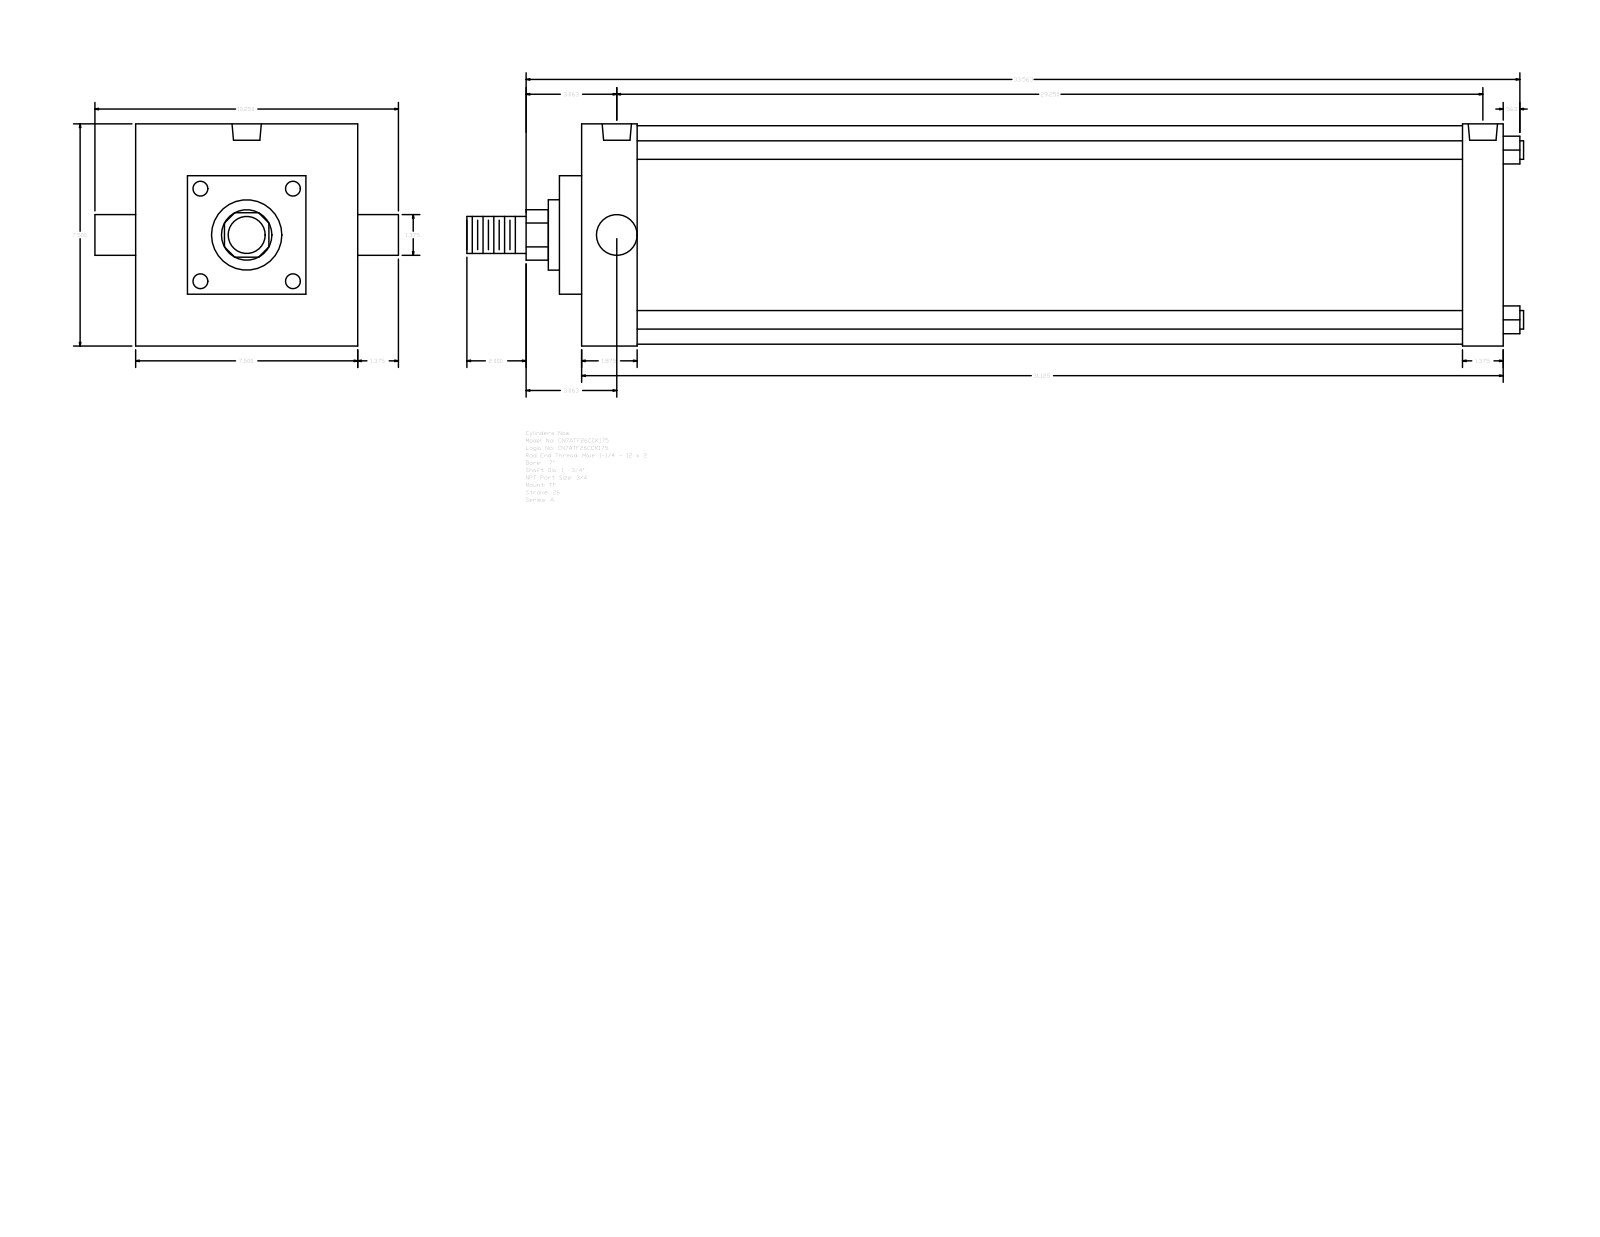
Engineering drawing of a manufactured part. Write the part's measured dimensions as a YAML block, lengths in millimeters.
part_name: "A_TF__0700_1.75"
step_written_by: "GSSL Pune (CONFIG_CONTROL_DESIGN)"
units: millimeters
bodies: {solids: 0, faces: 89, planar: 65, cylindrical: 24, other: 0}
overall_size: [906.46, 260.35, 190.5]
round_holes:
  - {diameter: 15.08, count: 3}
  - {diameter: 25.12, count: 2}
round_bosses_or_shafts:
  - {diameter: 15.88, count: 4}
  - {diameter: 187.32, count: 1}
  - {diameter: 60.33, count: 1}
  - {diameter: 44.45, count: 1}
  - {diameter: 34.92, count: 1}
  - {diameter: 31.75, count: 1}
partial_cylinders:
  - {radius: 21.63, count: 1}
face_to_face_distances: [190.5, 790.58, 34.93, 146.05, 19.05, 47.63, 742.95, 755.65, 708.02, 44.45]
hole_center_spacings: [5.56, 737.39, 731.83, 742.95]
